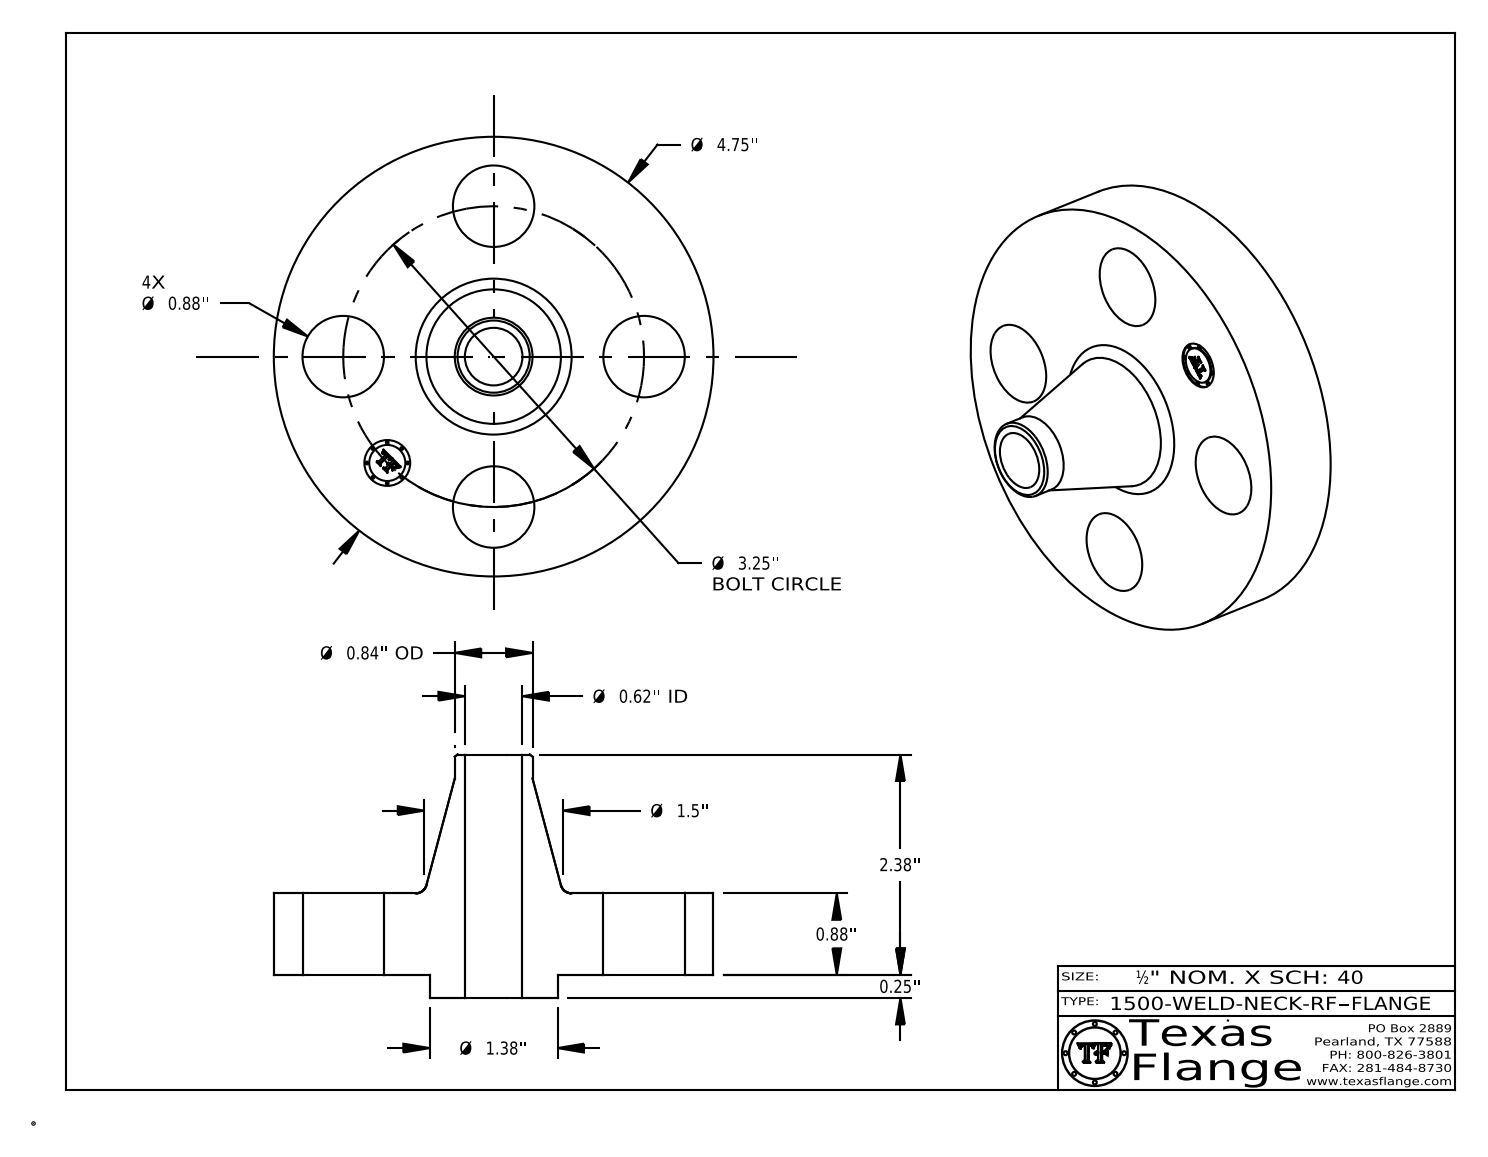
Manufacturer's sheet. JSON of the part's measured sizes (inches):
{"part_name": "1500-WELD-NECK-RF", "step_written_by": "CATIA V5 STEP AP214 (AUTOMOTIVE_DESIGN)", "units": "inches", "bodies": {"solids": 1, "faces": 411, "planar": 369, "cylindrical": 36, "other": 6}, "overall_size": [4.75, 4.75, 2.63], "volume_in3": 14.55, "surface_area_in2": 63.17, "round_holes": [[0.88, 4], [0.495, 1], [0.622, 1]], "round_bosses_or_shafts": [[0.03, 8], [4.75, 1], [1.38, 1], [0.84, 1], [0.39, 1]], "face_to_face_distances": [0.88, 0.25, 1.13, 2.63, 2.38, 1.5, 1.115, 0.865, 0.015, 1.515], "hole_center_spacings": [1.625, 2.298, 1.244, 3.003, 3.25]}
